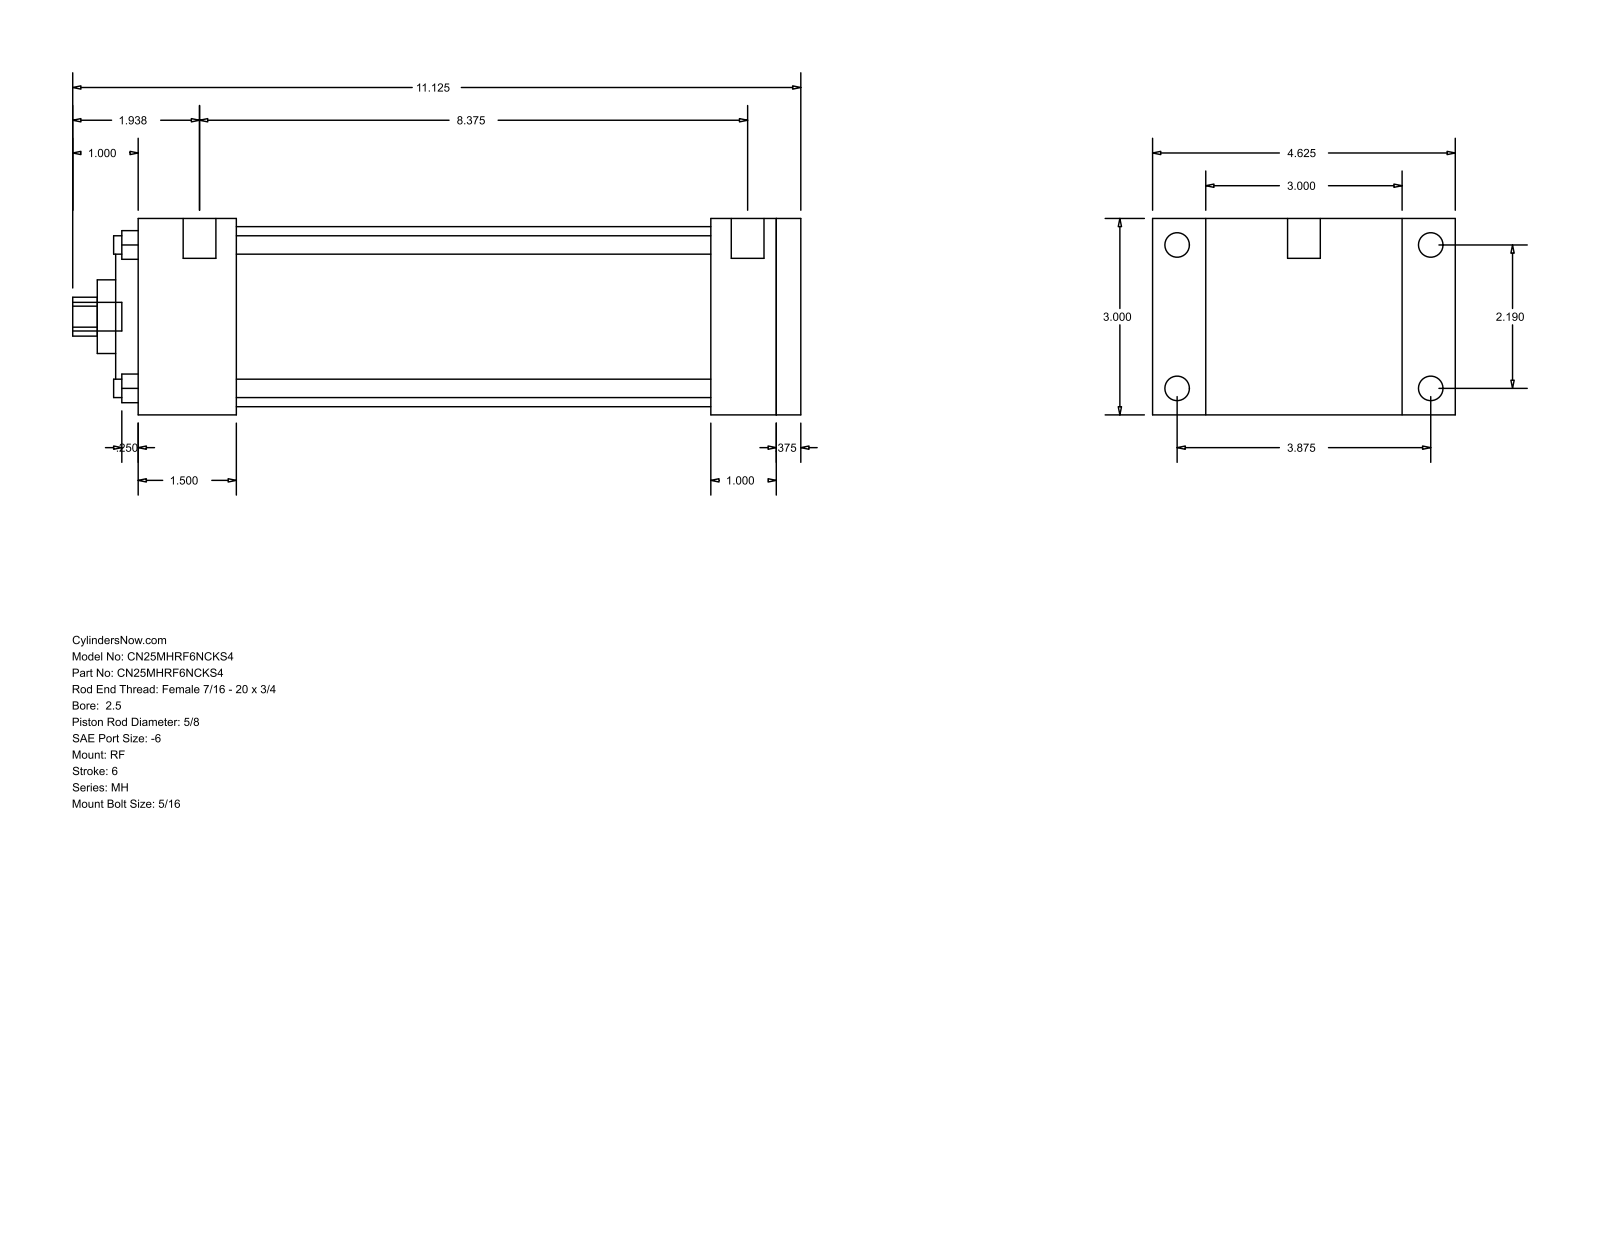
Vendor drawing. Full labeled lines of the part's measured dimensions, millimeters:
Part name (STEP PRODUCT): MH_RF__0250_0.625
STEP written by: GSSL Pune (CONFIG_CONTROL_DESIGN)
Units: millimetres
Bodies: 0 solids, 94 faces (65 planar, 29 cylindrical, 0 other)
Overall size (bounding box): 282.57 × 117.47 × 76.2
Round holes (diameter × count): ⌀7.14 ×4, ⌀15.88 ×1, ⌀28.57 ×1, ⌀55.55 ×1, ⌀69.85 ×1
Round bosses / shafts (diameter × count): ⌀9.53 ×4, ⌀5.56 ×4, ⌀12.7 ×2, ⌀11.11 ×1
Partial cylindrical surfaces — rounded edges, fillets, slot ends (radius × count): R7.54 ×1
Main face-to-face distances: 76.2, 9.52, 257.17, 247.65, 25.4, 222.25, 34.92, 38.1, 184.15, 209.55
Hole centre spacings: 39.33, 55.62, 78.66
